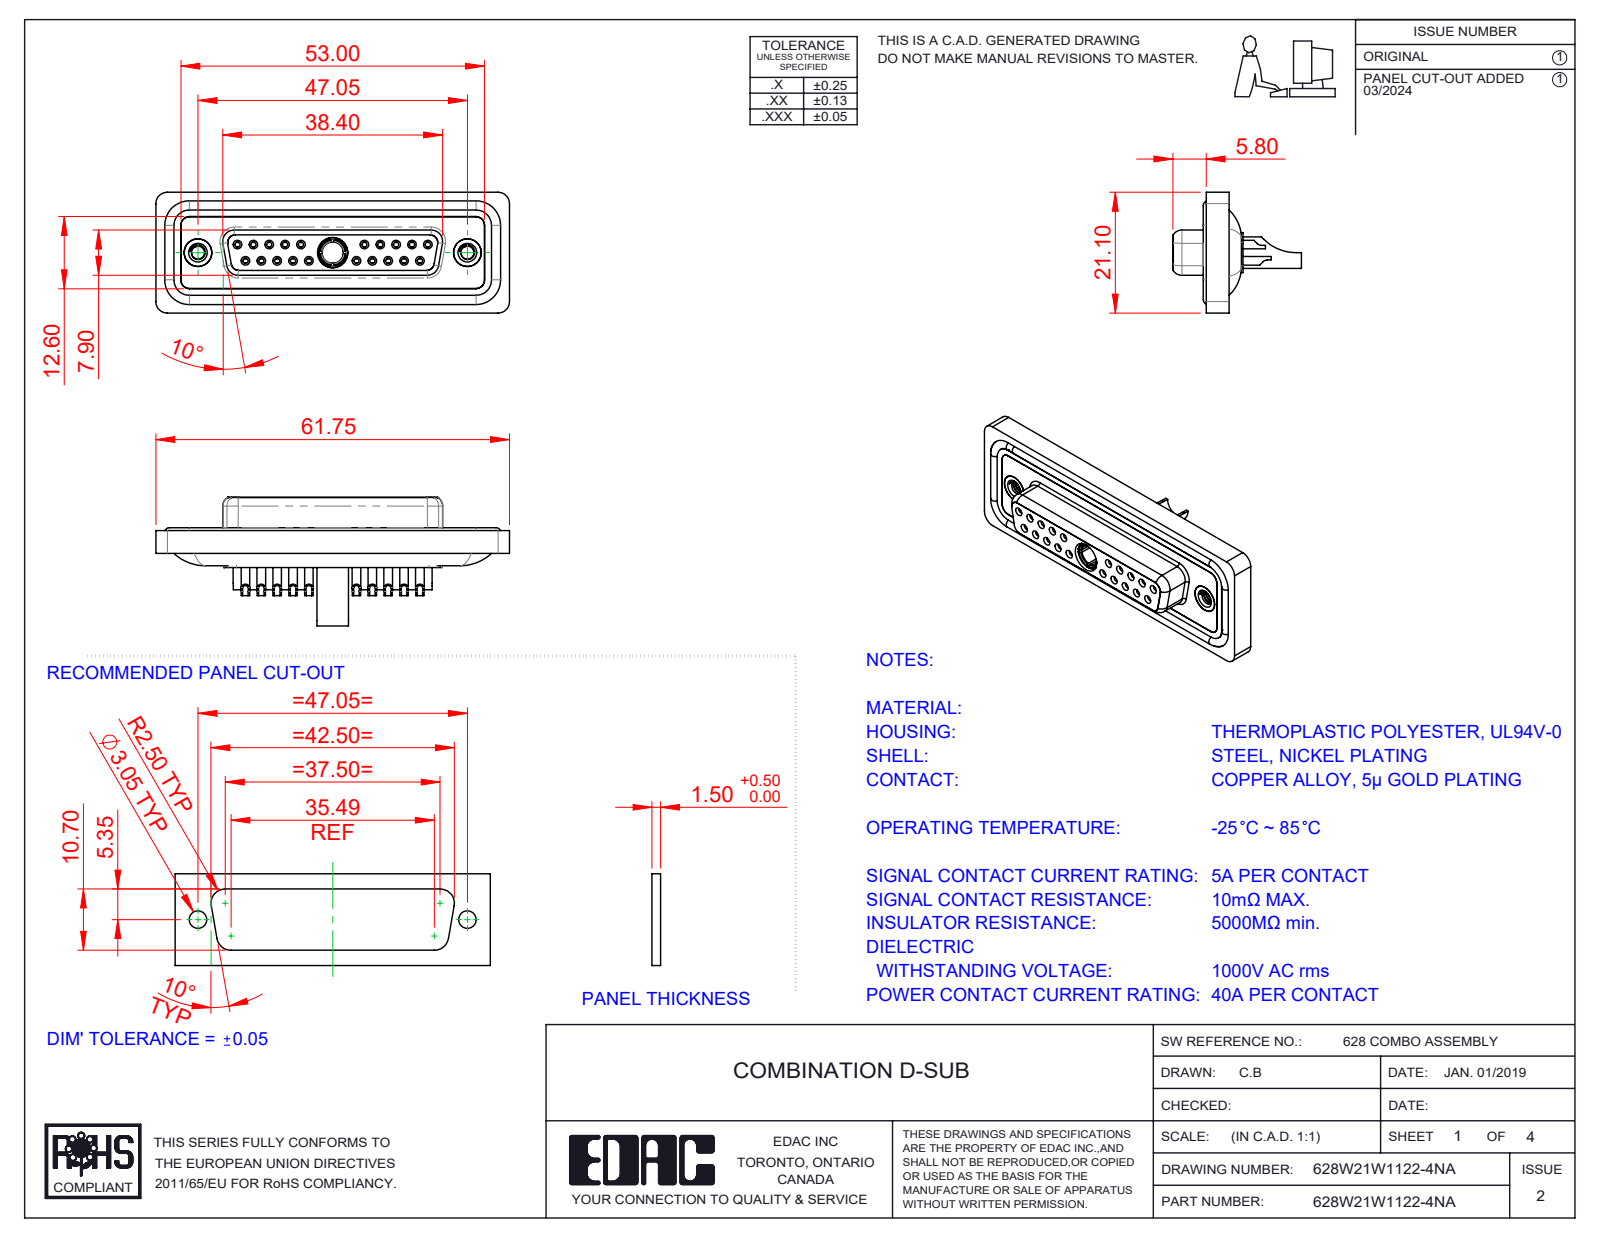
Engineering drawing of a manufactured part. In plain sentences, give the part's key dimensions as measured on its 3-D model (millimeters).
The part is named "628Combo Threaded Rivet_A; 628Combo Contact Row 1_22; 628Combo Housing_21W1; 628Combo Waterproof Housing_25 Contacts (+5 more)". Its 3-D file was written by "SolidWorks 2023 (CONFIG_CONTROL_DESIGN)". It is 29 solids with 1561 faces: 476 planar, 634 cylindrical and 451 other. Overall it measures 61.75 by 22.45 by 21.1 millimeters. Its volume is 8 456 cubic millimeters and its surface area 14 349 square millimeters. Round holes: 20 of diameter 0.9, 20 of diameter 1, 20 of diameter 1.1, 20 of diameter 1.5, 20 of diameter 2, 10 of diameter 1.6, 10 of diameter 1.7, 3 of diameter 4.85, 2 of diameter 2.26, 2 of diameter 4, 2 of diameter 4.05, 2 of diameter 5. Round bosses or shafts: 20 of diameter 2.2, 14 of diameter 1.6, 2 of diameter 4.95, 2 of diameter 4.8, 1 of diameter 5.5, 1 of diameter 5.2, 1 of diameter 4.96, 1 of diameter 4.75. Partial cylindrical surfaces (rounded edges, fillets, slot ends): 22 of radius 1.5, 18 of radius 2, 8 of radius 1.35, 8 of radius 1.6, 6 of radius 1, 4 of radius 0.25, 4 of radius 0.5, 4 of radius 0.6. The main face-to-face distances are 0.4, 1.8, 7.45, 5.65, 6.6, 0.5, 1.6, 7.05, 2.9, 1.1. The hole center spacings are 3.16, 2.77, 5.54, 5.03, 8.31, 7.48, 16.62, 19.39.
